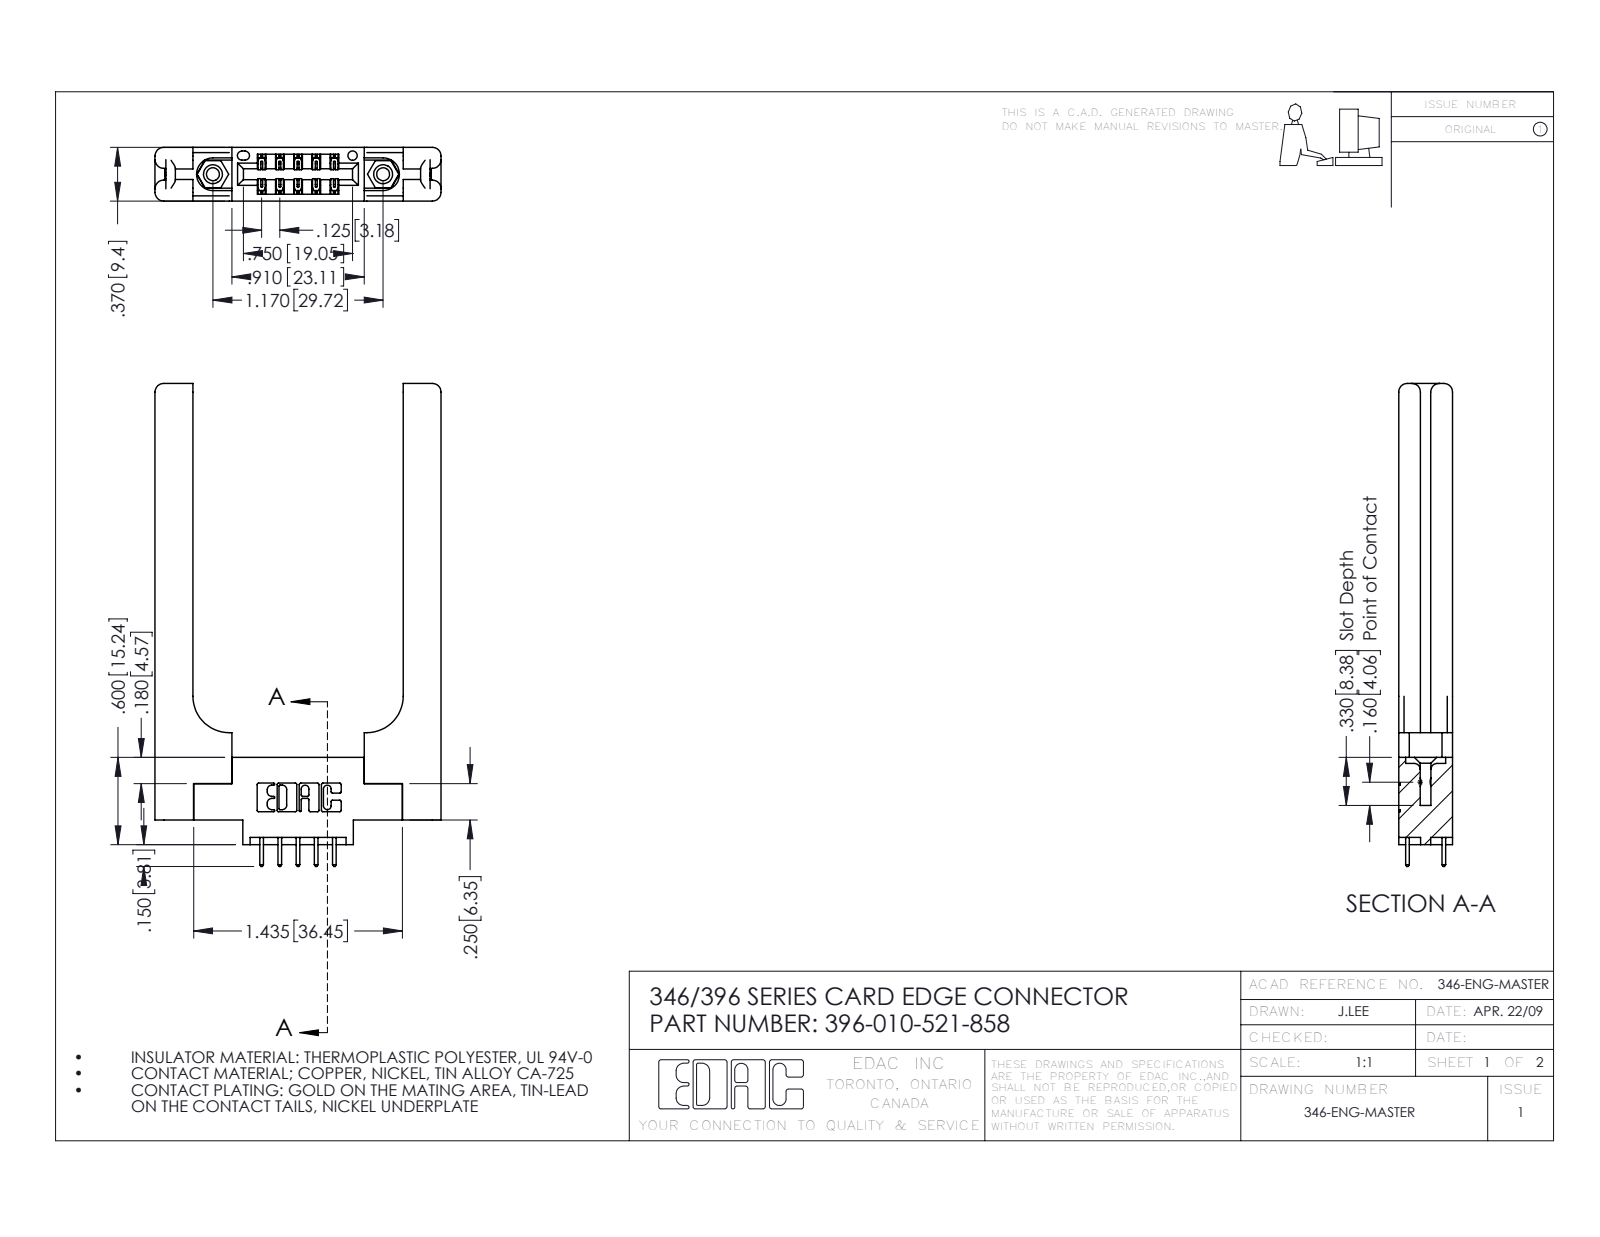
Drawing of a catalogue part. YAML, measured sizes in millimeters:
part_name: "345-292-001_345-293-121; 346-220-058_345-220-058; 396-010-521-858; 345-250-001_345-250-001-102 (+1 more)"
step_written_by: "SolidWorks 2016 (CONFIG_CONTROL_DESIGN)"
units: millimeters
bodies: {solids: 15, faces: 902, planar: 578, cylindrical: 264, other: 60}
overall_size: [84.3, 49.9, 9.4]
volume: 11900
surface_area: 10630
round_holes:
  - {diameter: 2.3, count: 2}
  - {diameter: 3.2, count: 2}
  - {diameter: 4, count: 2}
  - {diameter: 1.6, count: 1}
round_bosses_or_shafts:
  - {diameter: 3.9, count: 2}
partial_cylinders:
  - {radius: 0.3, count: 22}
  - {radius: 1.5, count: 16}
  - {radius: 0.2, count: 15}
  - {radius: 0.3, count: 10}
  - {radius: 0.2, count: 6}
  - {radius: 0.8, count: 6}
  - {radius: 0.7, count: 3}
  - {radius: 0.4, count: 2}
face_to_face_distances: [9.4, 3.8, 5.6, 6.4, 1.8, 36.7, 3.8, 1.9, 1.8, 2.6]
hole_center_spacings: [6.2, 24.6, 29.7]
